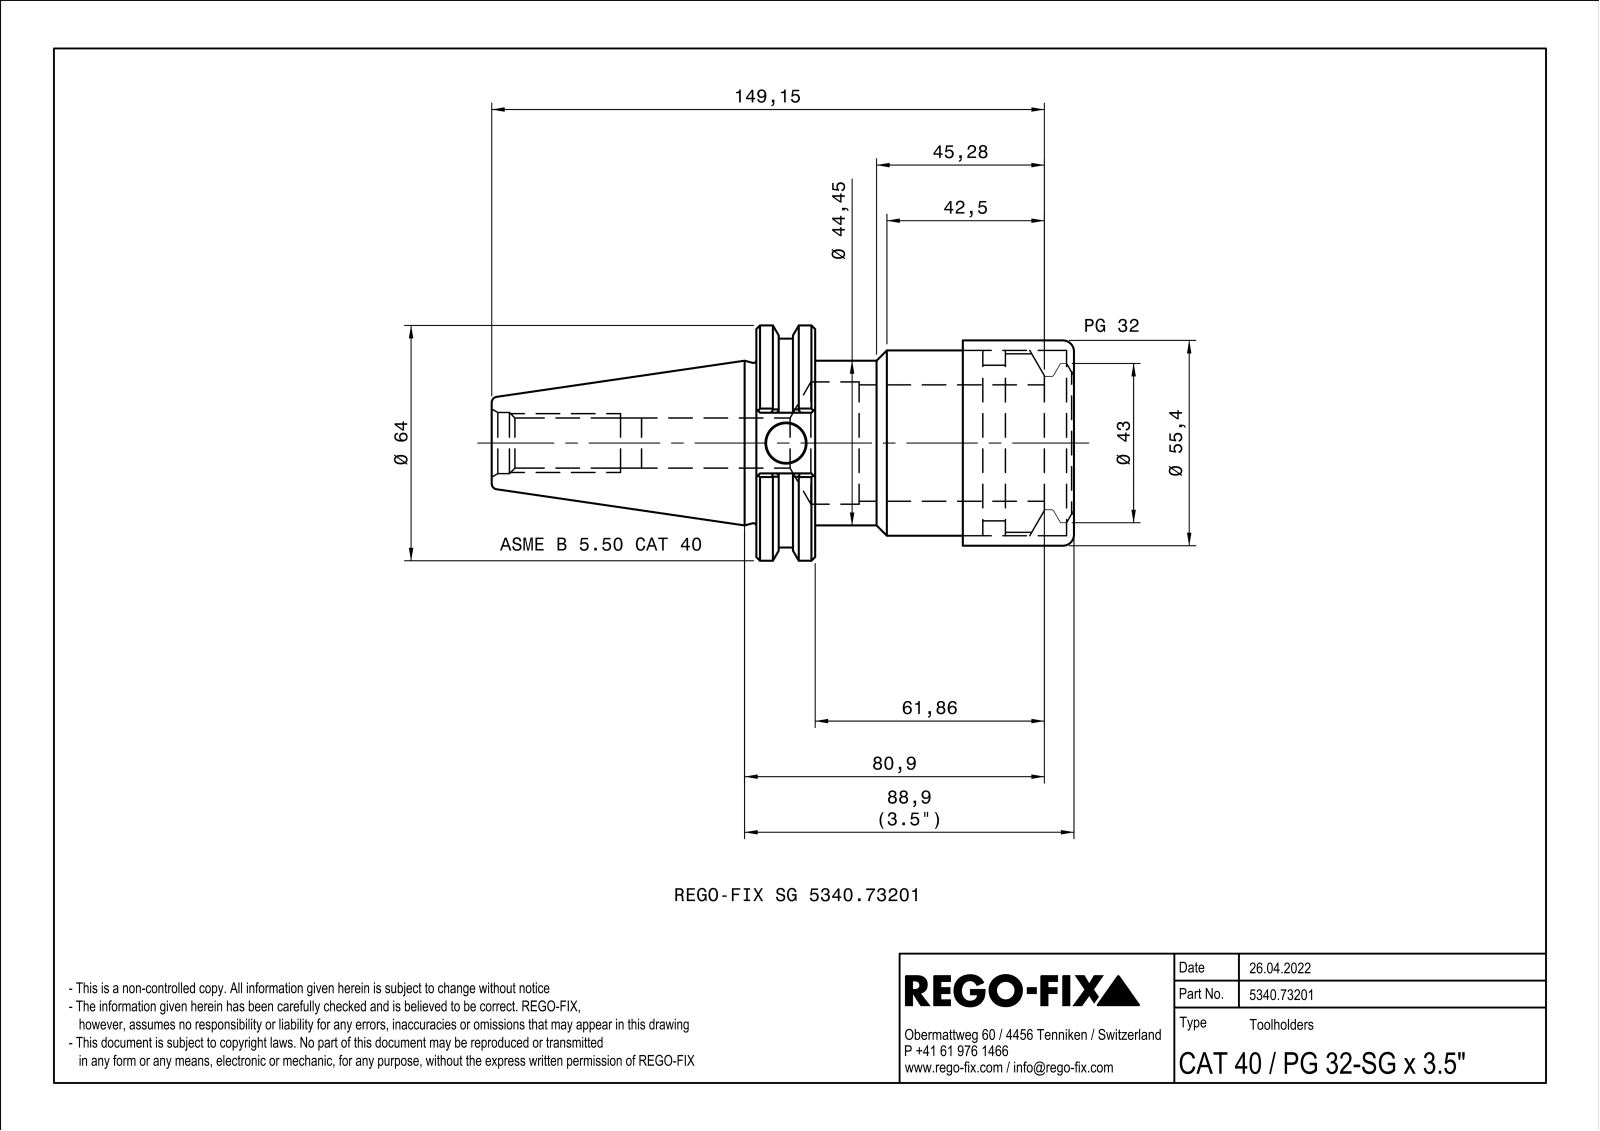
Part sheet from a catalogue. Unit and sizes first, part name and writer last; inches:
Units: inches
Overall size (bounding box): 6.187 × 2.5 × 2.393
Round holes (diameter × count): ⌀0.421 ×1, ⌀0.533 ×1, ⌀0.65 ×1, ⌀1.299 ×1, ⌀1.506 ×1, ⌀1.905 ×1, ⌀1.97 ×1, ⌀2.008 ×1
Round bosses / shafts (diameter × count): ⌀2.5 ×1, ⌀2.219 ×1, ⌀2.181 ×1, ⌀2.165 ×1, ⌀1.969 ×1, ⌀1.75 ×1, ⌀1.654 ×1
Partial cylindrical surfaces — rounded edges, fillets, slot ends (radius × count): R0.02 ×4
Main face-to-face distances: 0.625, 2.75, 3.375, 0.969, 1.782, 2.407, 0.728, 0.24, 2.022, 2.647
Volume: 10.34 in³ · Surface area: 72.09 in²
Bodies: 1 solid, 106 faces (36 planar, 23 cylindrical, 47 other)
Part name (STEP PRODUCT): NOCUT
STEP written by: SIEMENS PLM Software Solid Edge ST10 (AUTOMOTIVE_DESIGN)
